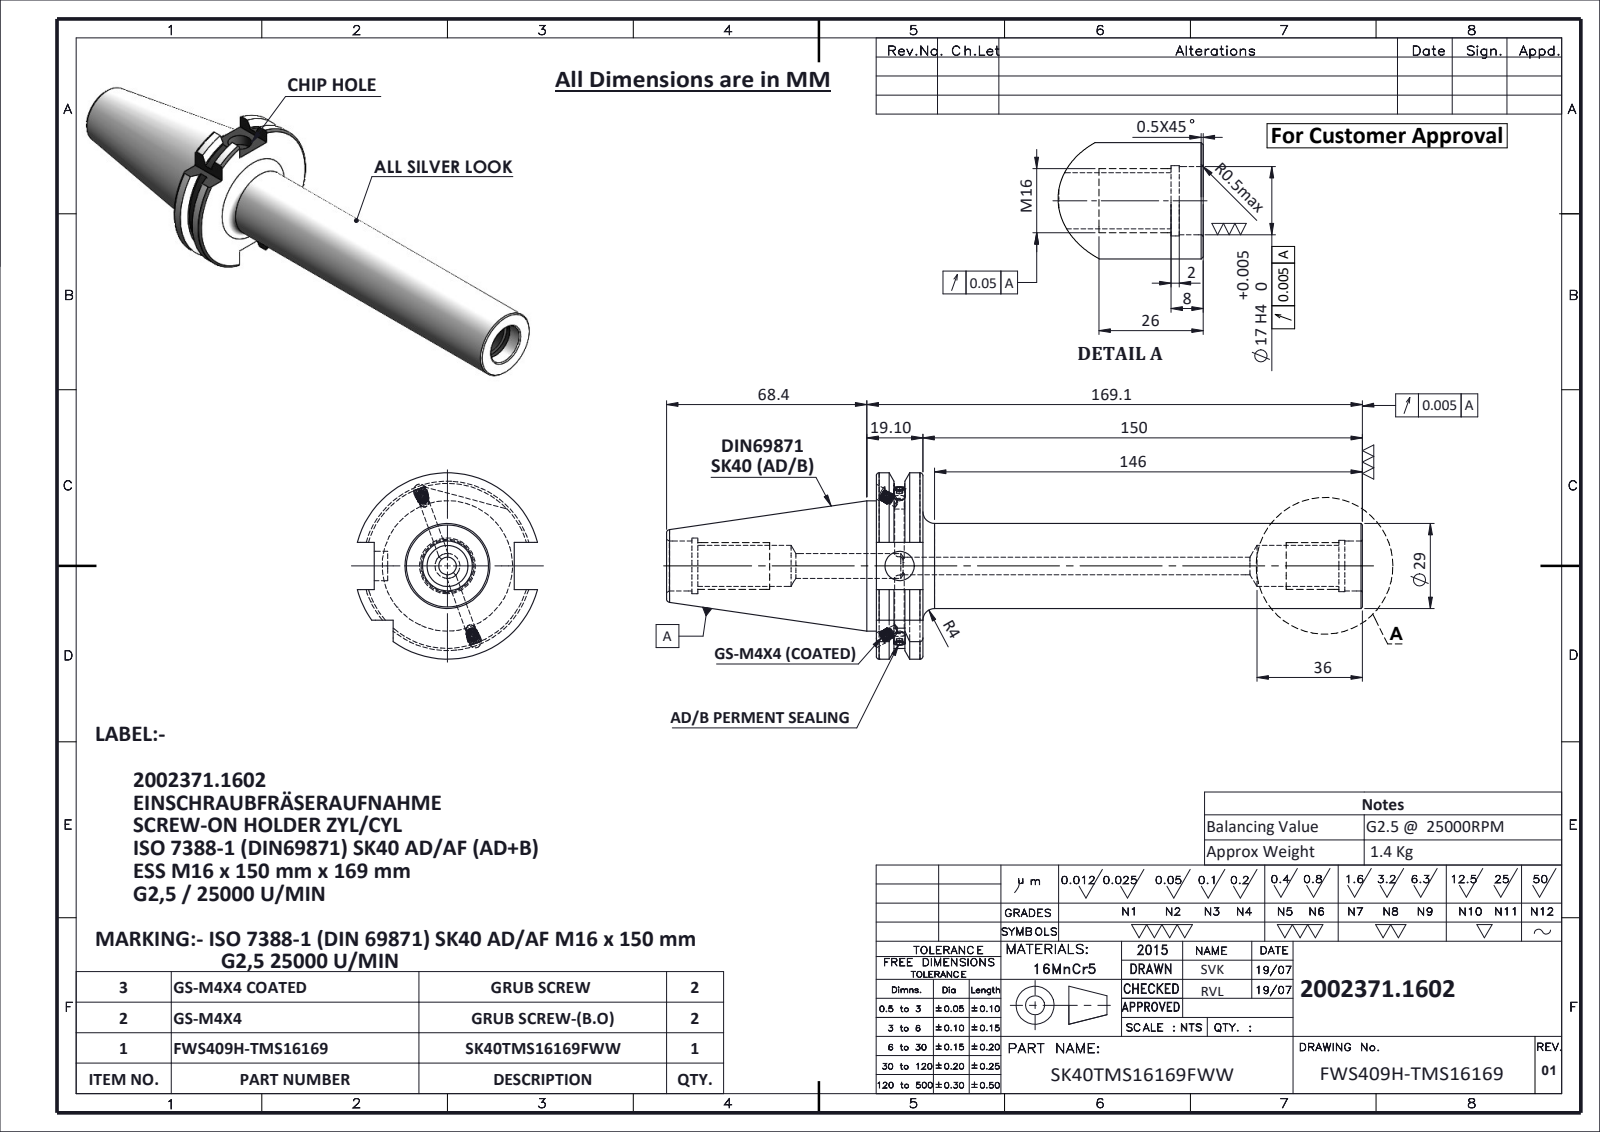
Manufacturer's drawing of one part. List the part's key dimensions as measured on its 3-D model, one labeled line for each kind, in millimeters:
Part name (STEP PRODUCT): SK40TMS16169FWW; FWS409H-TMS16169; GS-M4X4-COATING_DIN 913 - M4 x 4-N; GS-M4X4_DIN 913 - M4 x 4-N
STEP written by: SolidWorks 2024 (CONFIG_CONTROL_DESIGN)
Units: millimetres
Bodies: 5 solids, 247 faces (64 planar, 74 cylindrical, 109 other)
Overall size (bounding box): 237.5 × 63.55 × 61.48
Volume: 192 794 mm³ · Surface area: 38 331 mm²
Round holes (diameter × count): ⌀3.3 ×3, ⌀4.5 ×2, ⌀6 ×1, ⌀8.5 ×1, ⌀10 ×1, ⌀14 ×1, ⌀17 ×1, ⌀17.5 ×1, ⌀19 ×1
Round bosses / shafts (diameter × count): ⌀4 ×4, ⌀2.9 ×2, ⌀44.45 ×1, ⌀29 ×1
Partial cylindrical surfaces — rounded edges, fillets, slot ends (radius × count): R28.12 ×1, R31.77 ×1
Main face-to-face distances: 15.9, 165.9, 150, 16.1, 47.8, 71.6, 87.5, 237.5, 10.7, 60.9
